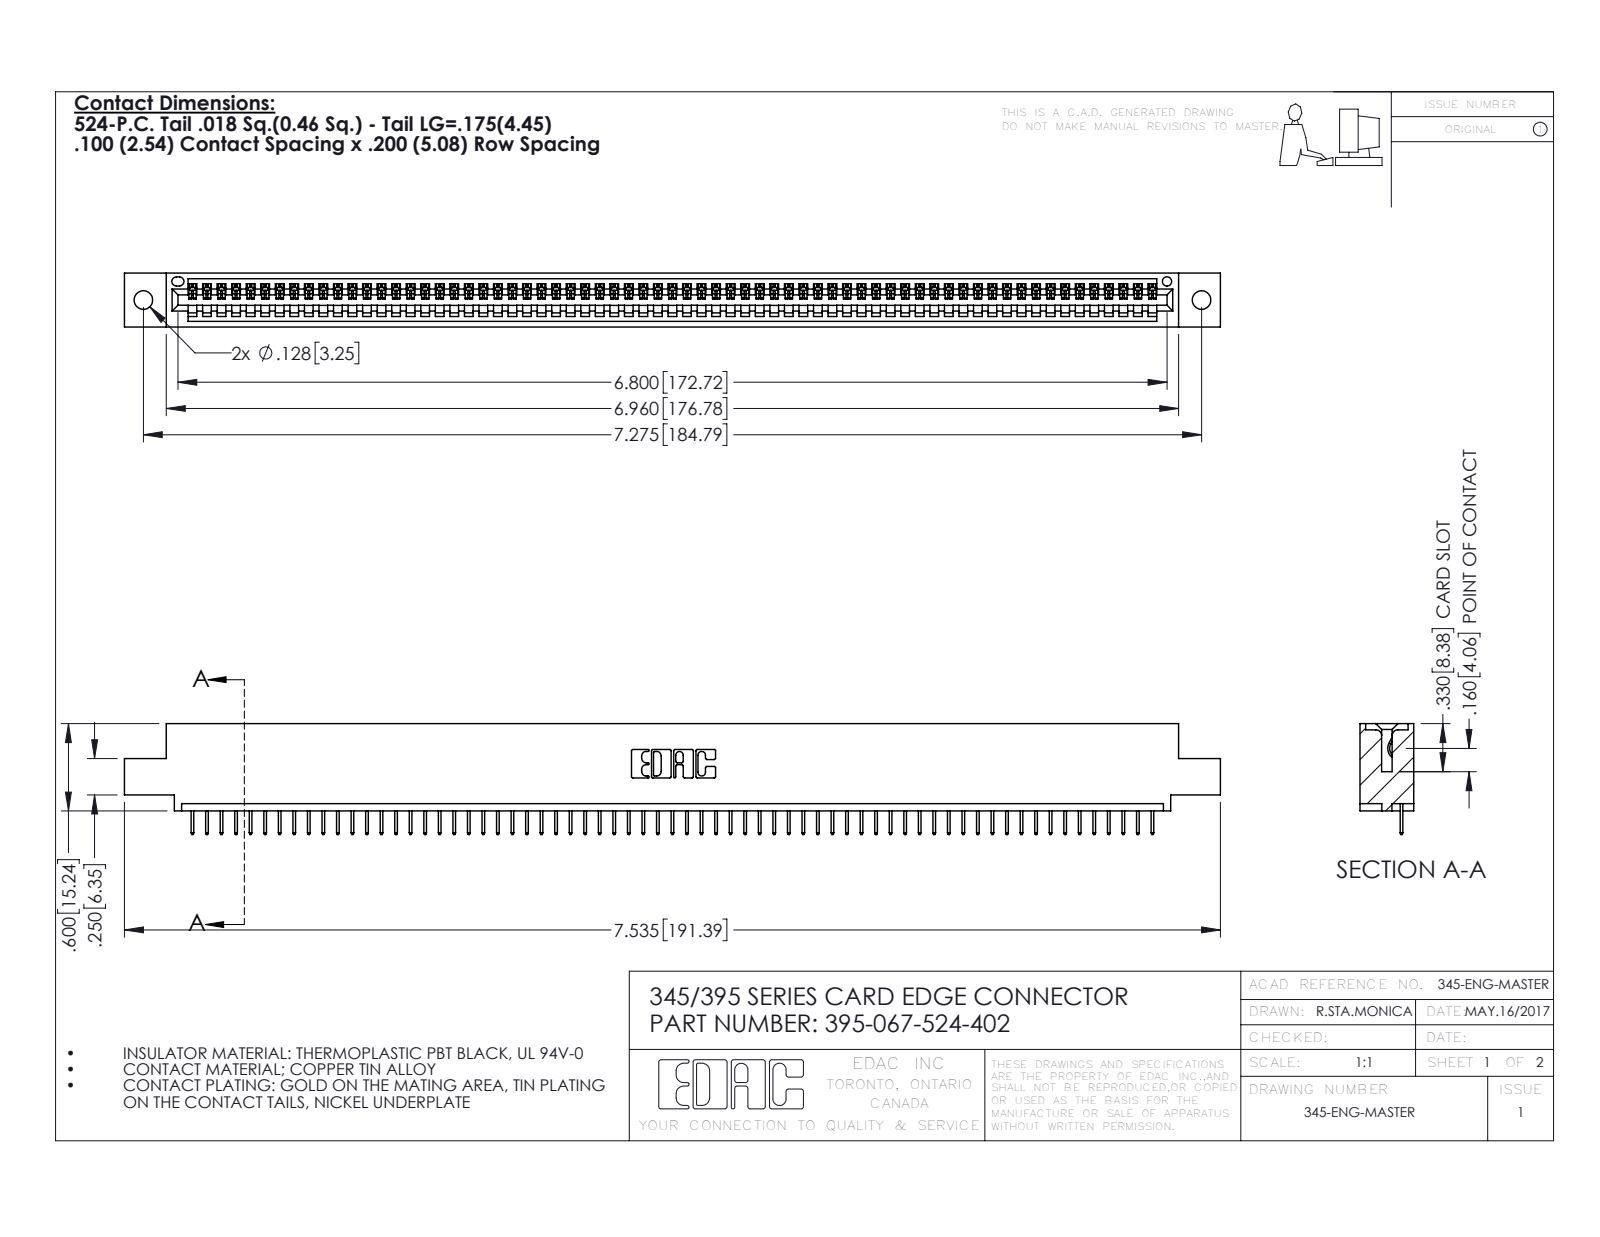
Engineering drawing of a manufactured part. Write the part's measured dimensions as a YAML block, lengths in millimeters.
part_name: "345 Part_0.110 Offset - 0.128 Dia; 395-067-524-402; 345-292-001_345-293-124"
step_written_by: "SolidWorks 2016 (CONFIG_CONTROL_DESIGN)"
units: millimeters
bodies: {solids: 68, faces: 4284, planar: 3166, cylindrical: 1118, other: 0}
overall_size: [191.4, 19.4, 9.4]
volume: 18010
surface_area: 23240
round_holes:
  - {diameter: 3.3, count: 2}
  - {diameter: 1.6, count: 1}
partial_cylinders:
  - {radius: 0.2, count: 134}
  - {radius: 0.3, count: 22}
  - {radius: 0.2, count: 6}
  - {radius: 0.8, count: 6}
  - {radius: 0.7, count: 3}
  - {radius: 0.8, count: 2}
  - {radius: 1, count: 2}
  - {radius: 0.4, count: 1}
face_to_face_distances: [1.8, 7.6, 9.4, 5.1, 2.5, 6.9, 0.6, 5.7, 1.8, 3.8]
hole_center_spacings: [6.9, 178.8, 184.8]
